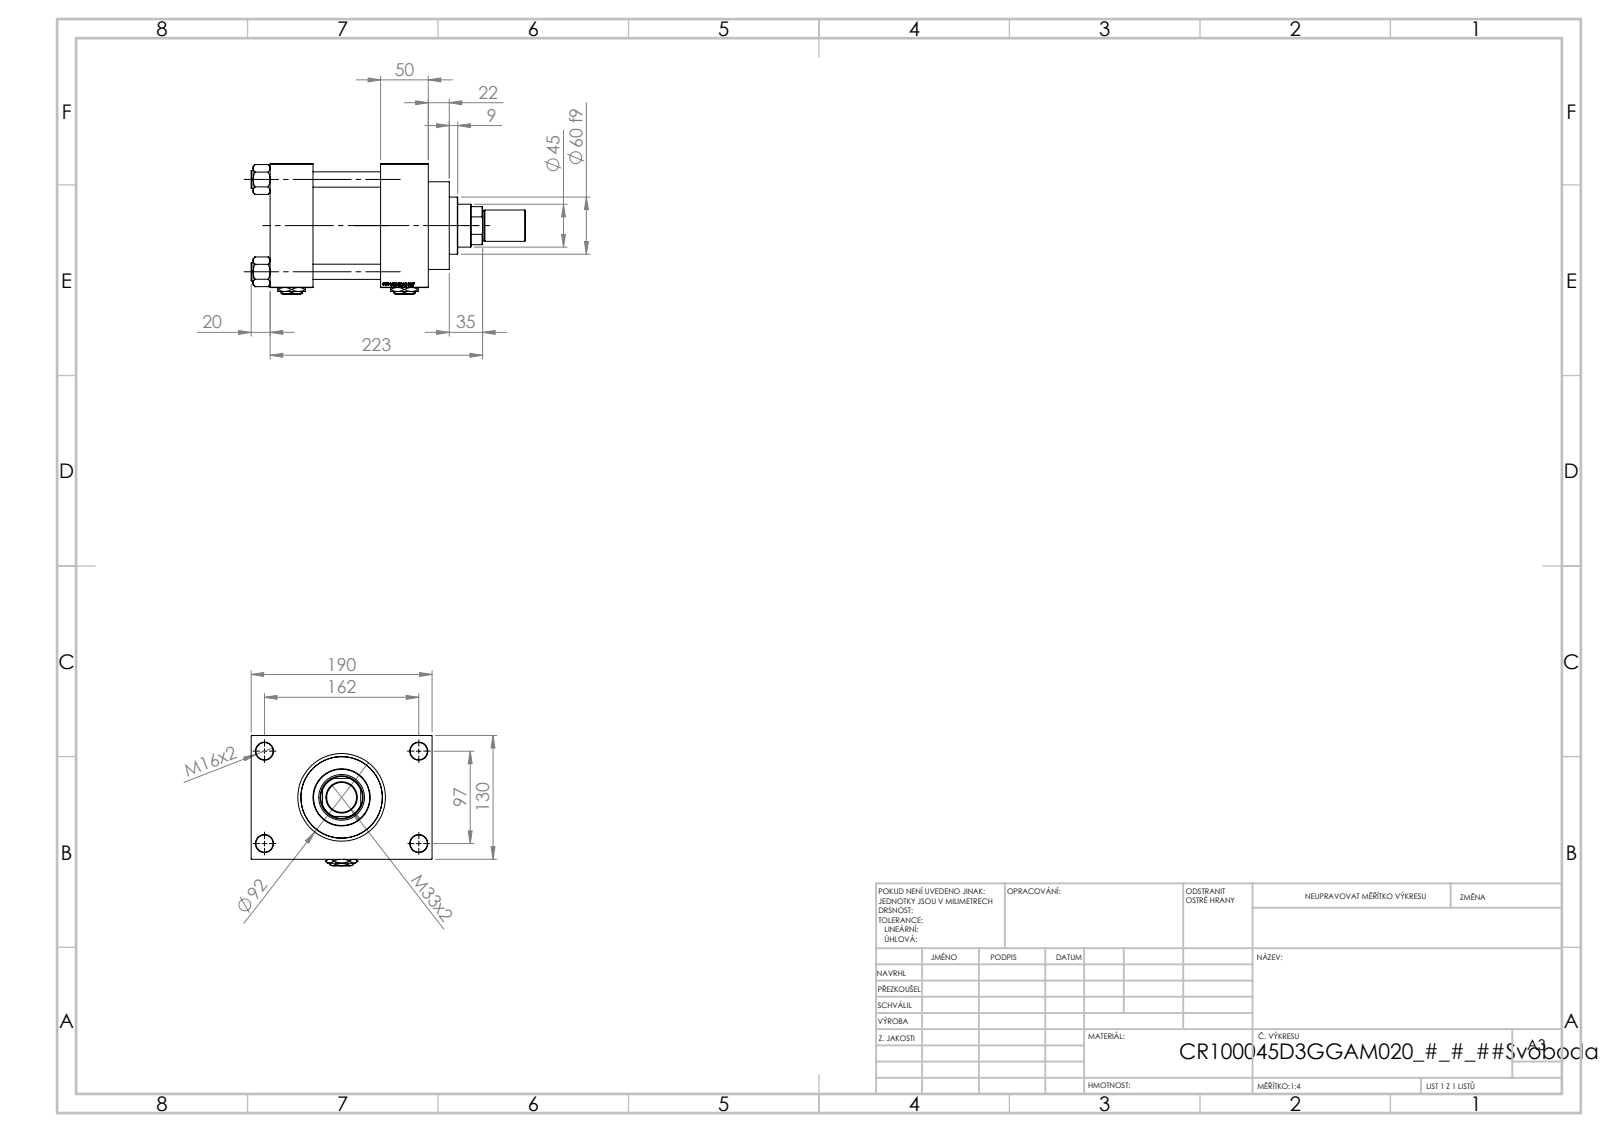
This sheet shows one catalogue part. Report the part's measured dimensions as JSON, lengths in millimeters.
{"part_name": "Zatka_pro_OIL_PORT; ROD_END_AH; V215CR_D_TYCINKA; V215CR_D_Body (+3 more)", "step_written_by": "SolidWorks 2019 (CONFIG_CONTROL_DESIGN)", "units": "millimeters", "bodies": {"solids": 14, "faces": 1267, "planar": 597, "cylindrical": 104, "other": 566}, "overall_size": [288, 190, 137], "volume_mm3": 2631000, "surface_area_mm2": 365776, "round_holes": [[16, 4], [18, 4], [7, 2], [26.44, 2], [35, 2], [31.5, 1], [45, 1], [48, 1], [76, 1], [85.5, 1], [100, 1]], "round_bosses_or_shafts": [[19, 4], [106, 1], [92, 1], [60, 1], [33, 1], [31, 1]], "partial_cylinders_radius": [[22, 1]], "face_to_face_distances": [45, 130, 116, 71, 166, 121, 50, 160, 30, 20], "hole_center_spacings": [32.55, 68.52, 94.41, 96.9, 102.27, 129.45, 161.73, 97]}
